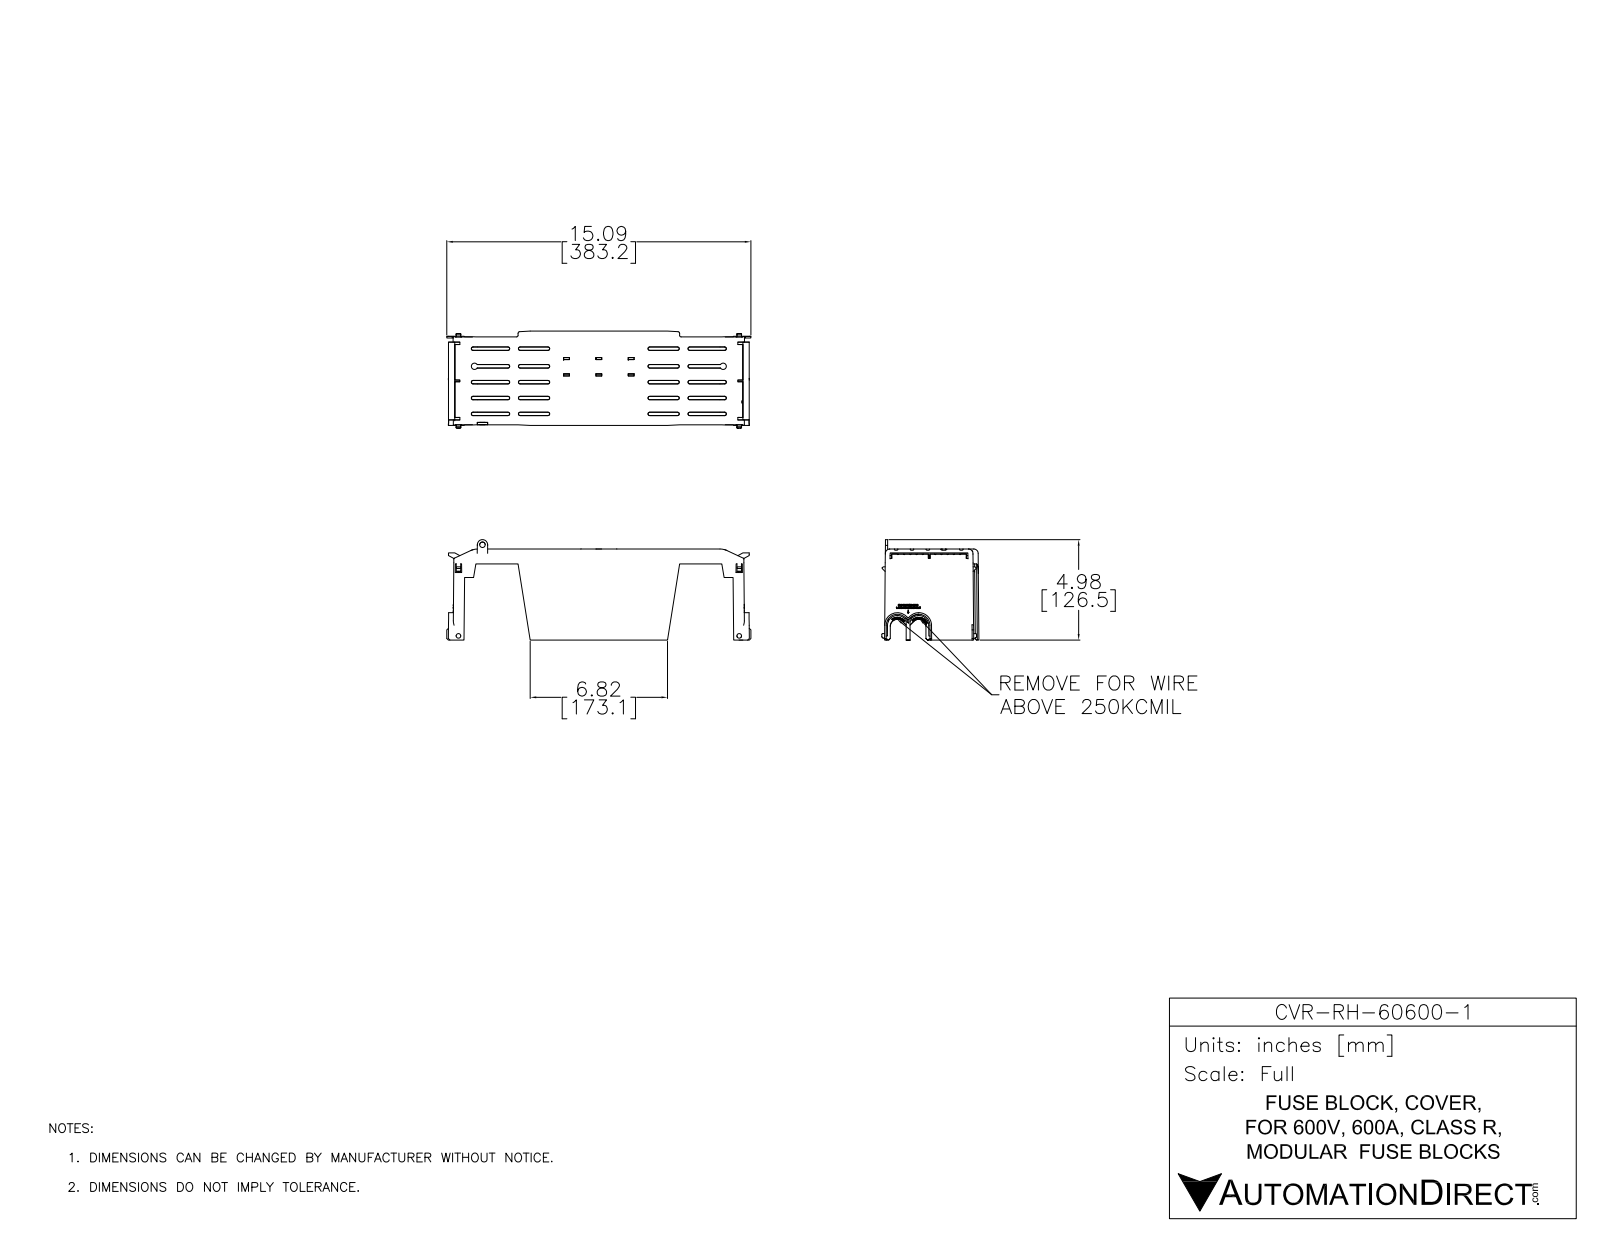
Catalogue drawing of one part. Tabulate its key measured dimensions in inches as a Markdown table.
| quantity | value |
| --- | --- |
| part name | CVR-RH-60600-1 |
| STEP written by | SolidWorks 2017 (AUTOMOTIVE_DESIGN) |
| units | inches |
| bodies | 1 solid, 2399 faces (1630 planar, 123 cylindrical, 646 other) |
| overall size | 15.085 × 4.983 × 4.817 |
| volume | 15.84 in³ |
| surface area | 413.6 in² |
| round holes (diameter × count) | 0.276 × 1 |
| round bosses / shafts (diameter × count) | 0.228 × 2 |
| partial cylindrical surfaces (radius × count) | 0.039 × 18, 0.118 × 8, 0.138 × 7, 0.217 × 7, 0.079 × 4, 0.354 × 4, 0.492 × 4, 0.551 × 4 |
| main face-to-face distances | 0.079, 0.256, 0.177, 0.795, 0.197, 0.335, 0.803, 0.118, 0.402, 1.598 |
